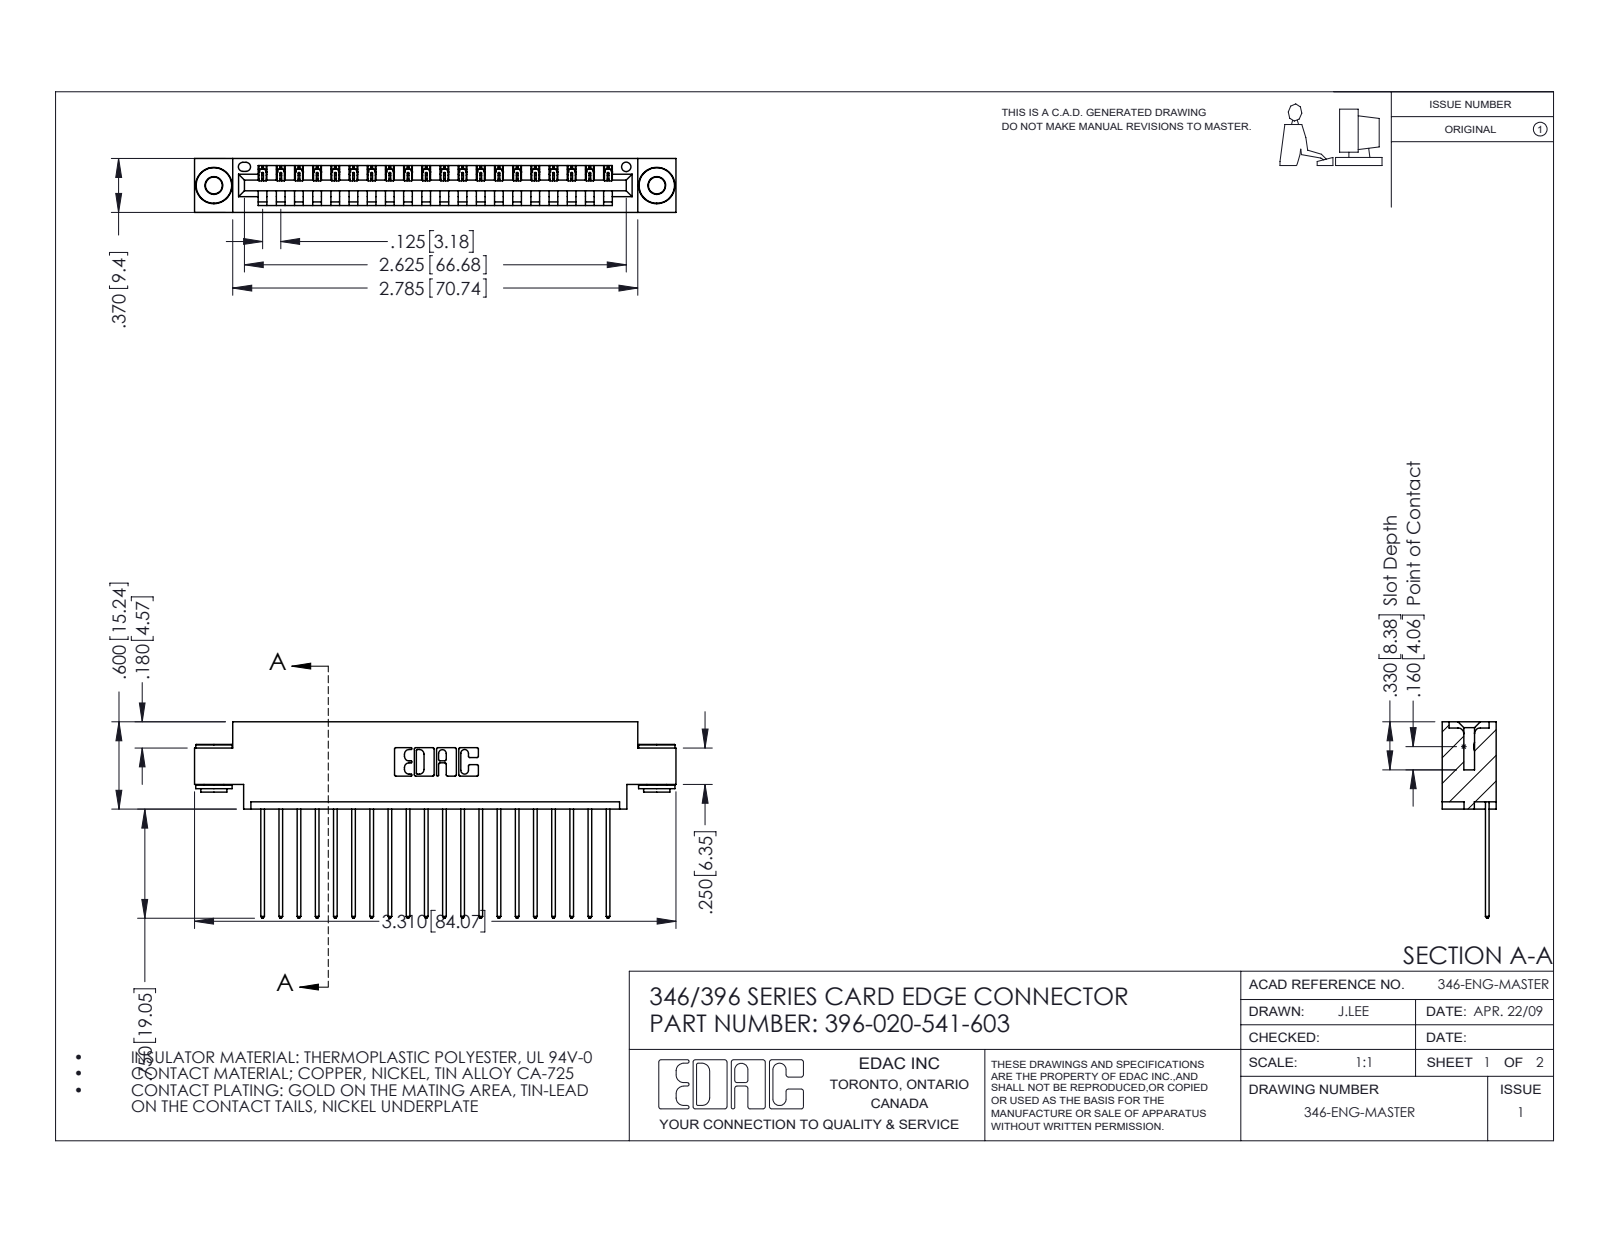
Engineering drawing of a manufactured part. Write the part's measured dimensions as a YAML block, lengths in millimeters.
part_name: "396-020-541-603; 346 Part_0.170 Offset - 0.156 Dia-TH; 345-292-001_345-293-141; 345-250-002_345-250-002-102"
step_written_by: "SolidWorks 2016 (CONFIG_CONTROL_DESIGN)"
units: millimeters
bodies: {solids: 23, faces: 1324, planar: 890, cylindrical: 426, other: 8}
overall_size: [84.1, 34.3, 9.4]
volume: 7830
surface_area: 10320
round_holes:
  - {diameter: 2.9, count: 2}
  - {diameter: 4, count: 2}
  - {diameter: 1.6, count: 1}
round_bosses_or_shafts:
  - {diameter: 6.4, count: 2}
  - {diameter: 4.6, count: 2}
  - {diameter: 3.5, count: 2}
partial_cylinders:
  - {radius: 0.2, count: 40}
  - {radius: 0.3, count: 40}
  - {radius: 0.3, count: 22}
  - {radius: 0.2, count: 6}
  - {radius: 0.8, count: 6}
  - {radius: 0.7, count: 3}
  - {radius: 0.8, count: 2}
  - {radius: 1, count: 2}
face_to_face_distances: [1.2, 8.2, 9.4, 6.4, 0.6, 1.8, 7.6, 3.8, 5.6, 2.5]
hole_center_spacings: [6.2, 72.1, 77.3]
